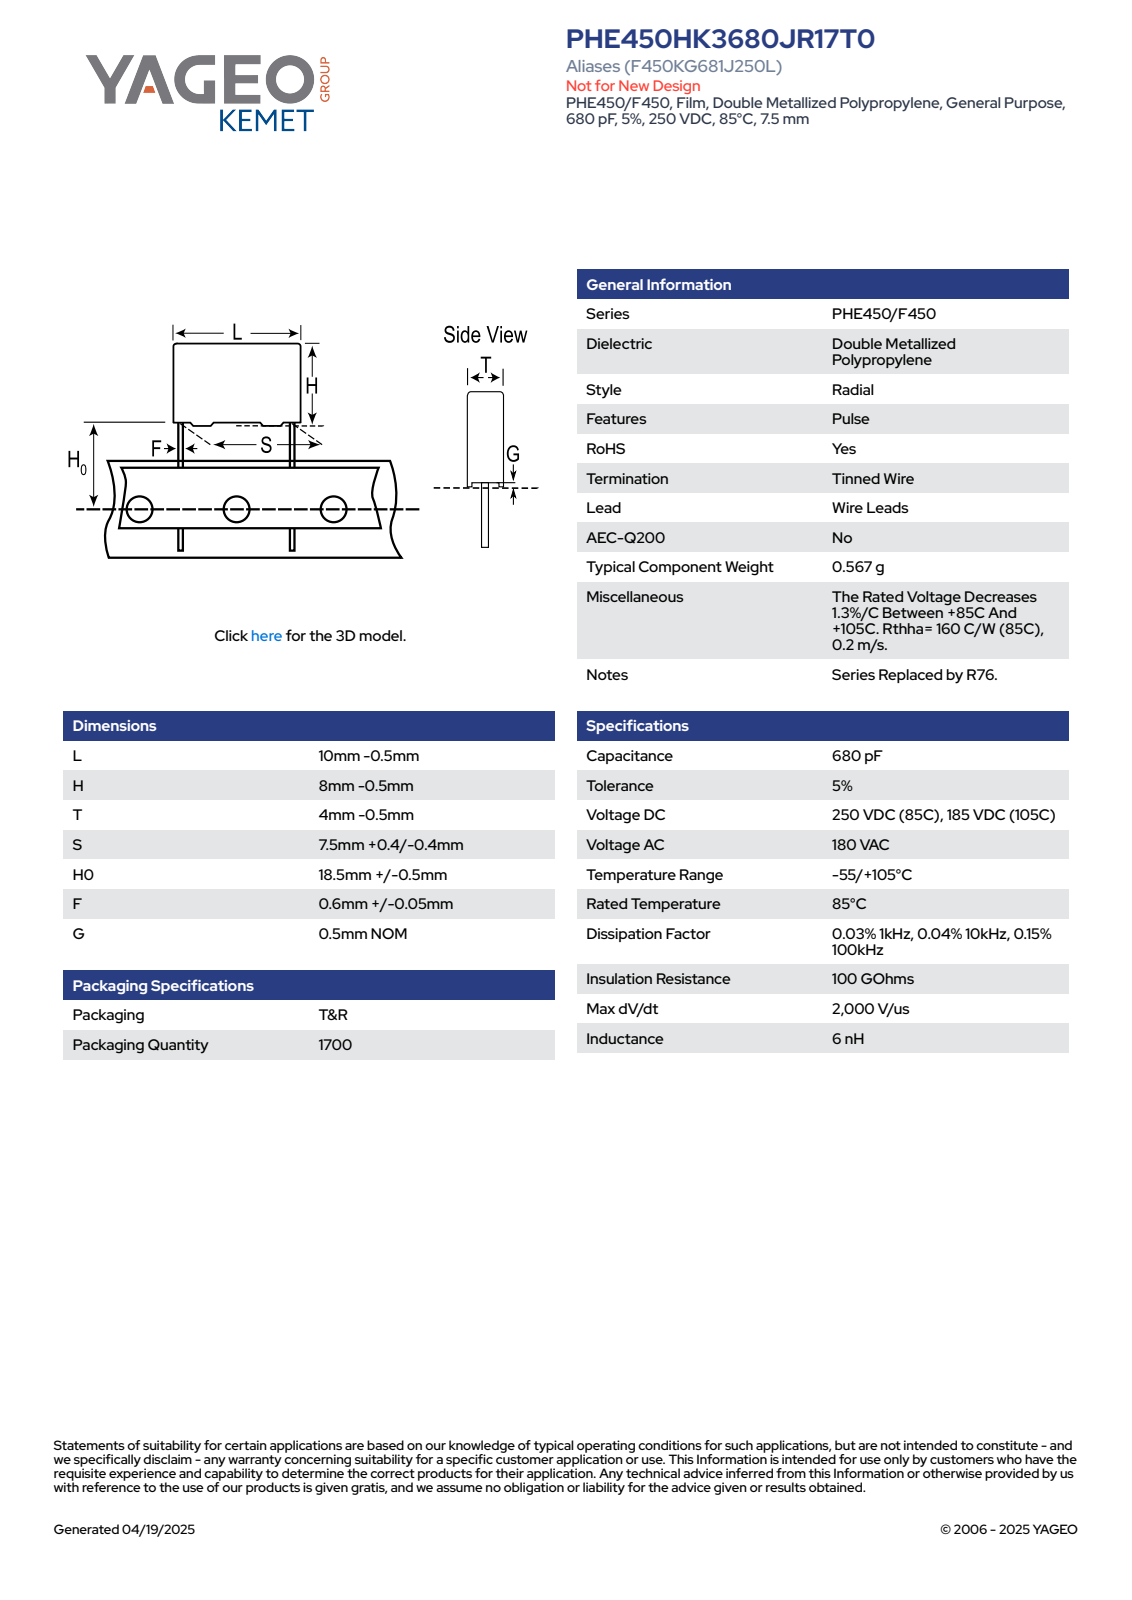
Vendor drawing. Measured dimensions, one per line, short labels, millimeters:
name: CFR_RBG_10X8X4_L9.5H7.5T3.5S7.5H019F0.65G0.5
written by: SolidWorks 2014 (AUTOMOTIVE_DESIGN)
unit: mm
bodies: 4 solids, 89 faces (81 planar, 8 cylindrical, 0 other)
size: 26.5 × 9.5 × 3.5
volume: 245 mm³; area: 339 mm²
bosses: 2× ⌀0.65
rounds: 4× R0.5
face distances: 3.5, 9.5, 7, 3.3, 3.1, 0.5, 7.5, 19, 19.5, 26.5
